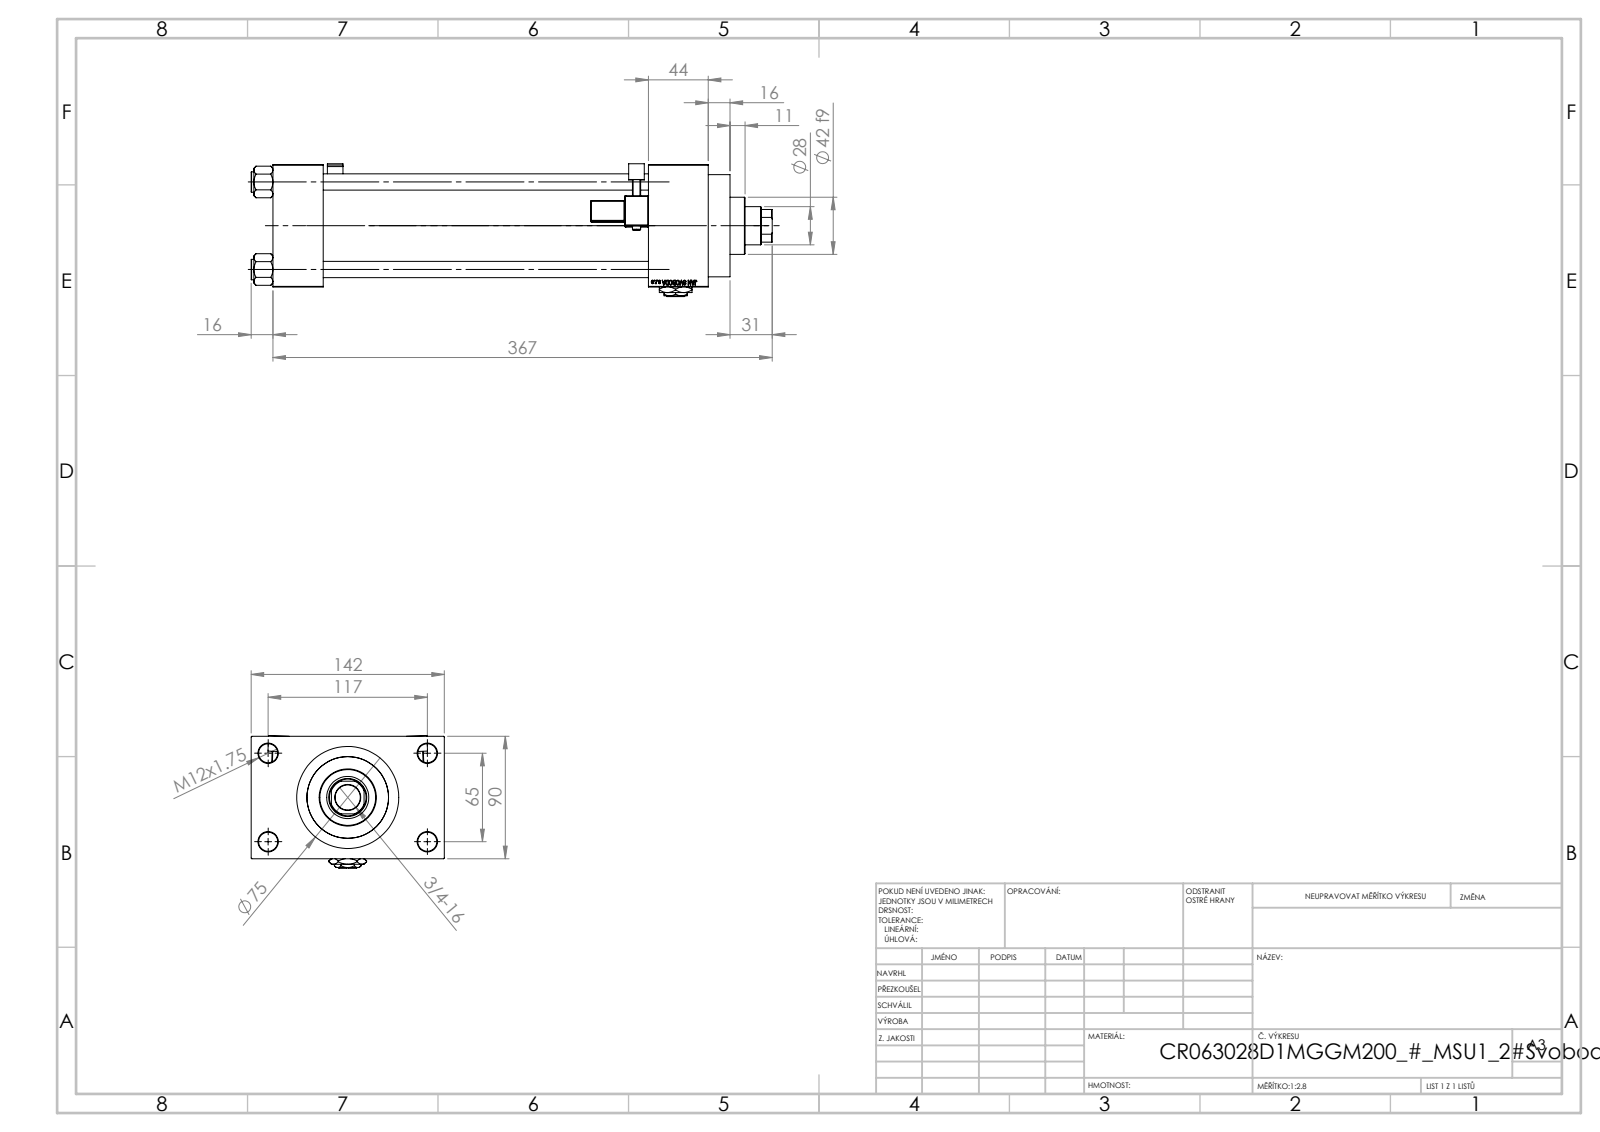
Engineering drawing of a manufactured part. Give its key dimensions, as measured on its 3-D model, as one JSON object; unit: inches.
{"part_name": "V215CR_VCP_D; V215CR_D_TYCINKA; Zatka_pro_OIL_PORT; V215CR_D_Body (+3 more)", "step_written_by": "SolidWorks 2019 (CONFIG_CONTROL_DESIGN)", "units": "inches", "bodies": {"solids": 14, "faces": 1306, "planar": 579, "cylindrical": 153, "other": 574}, "overall_size": [15.079, 5.591, 3.84], "volume_in3": 88.3, "surface_area_in2": 512, "round_holes": [[0.472, 4], [0.551, 4], [0.276, 2], [0.825, 2], [1.181, 2], [0.728, 1], [1.102, 1], [1.22, 1], [1.969, 1], [2.362, 1], [2.48, 1]], "round_bosses_or_shafts": [[0.591, 4], [0.236, 2], [2.953, 1], [2.717, 1], [1.654, 1]], "partial_cylinders_radius": [[0.02, 48], [0.039, 2], [0.098, 2], [0.157, 2], [0.531, 1]], "face_to_face_distances": [3.543, 9.409, 1.457, 10.866, 12.598, 11.142, 1.732, 1.024, 4.567, 5.591], "hole_center_spacings": [1.037, 1.79, 2.531, 2.635, 2.748, 3.569, 4.383, 2.559]}
